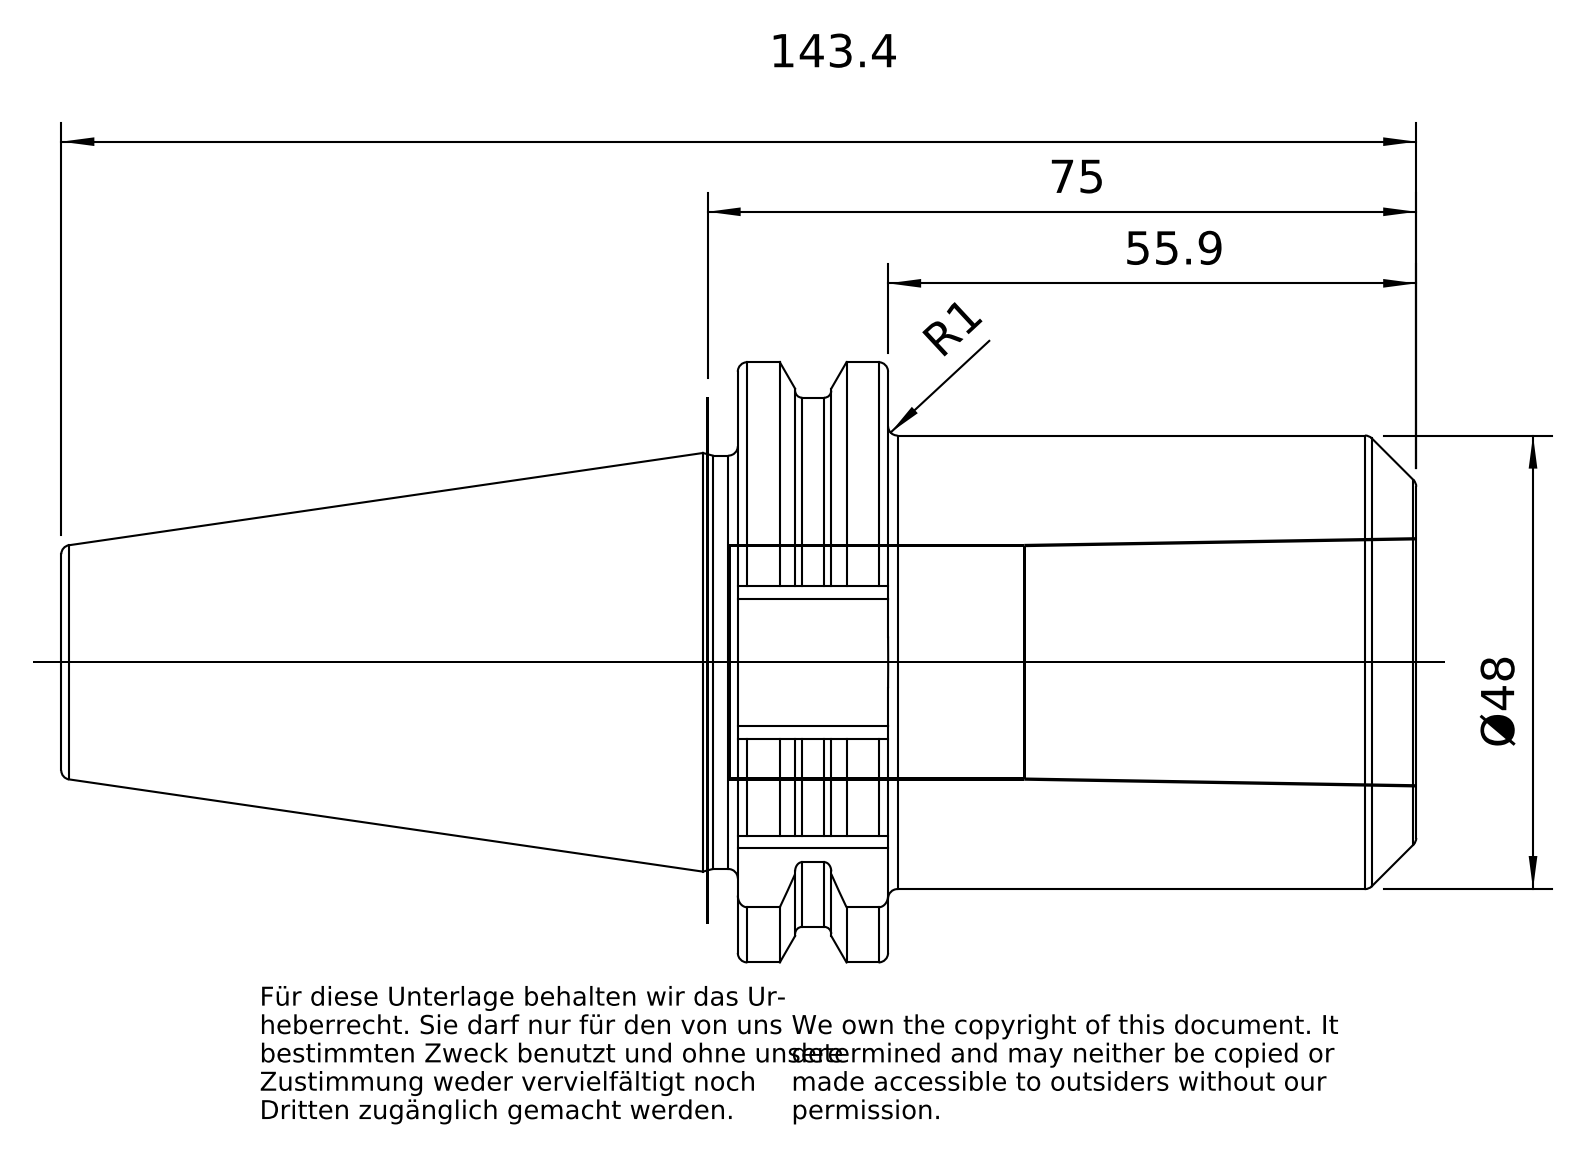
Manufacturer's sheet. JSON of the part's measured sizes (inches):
{"part_name": "40-420-03", "step_written_by": "PRO/ENGINEER BY PARAMETRIC TECHNOLOGY CORPORATION, 2010430 (CONFIG_CONTROL_DESIGN)", "units": "inches", "bodies": {"solids": 1, "faces": 102, "planar": 23, "cylindrical": 28, "other": 51}, "overall_size": [5.64, 2.501, 2.418], "volume_in3": 10.32, "surface_area_in2": 51.99, "round_holes": [[0.545, 1], [0.67, 1], [0.689, 1], [0.973, 1]], "round_bosses_or_shafts": [[1.89, 1], [1.722, 1], [0.63, 1]], "partial_cylinders_radius": [[0.053, 5], [1.102, 1], [1.25, 1]], "face_to_face_distances": [0.624, 2.827, 2.203, 0.035, 0.659, 2.862, 1.866, 0.638, 2.778, 2.813]}
